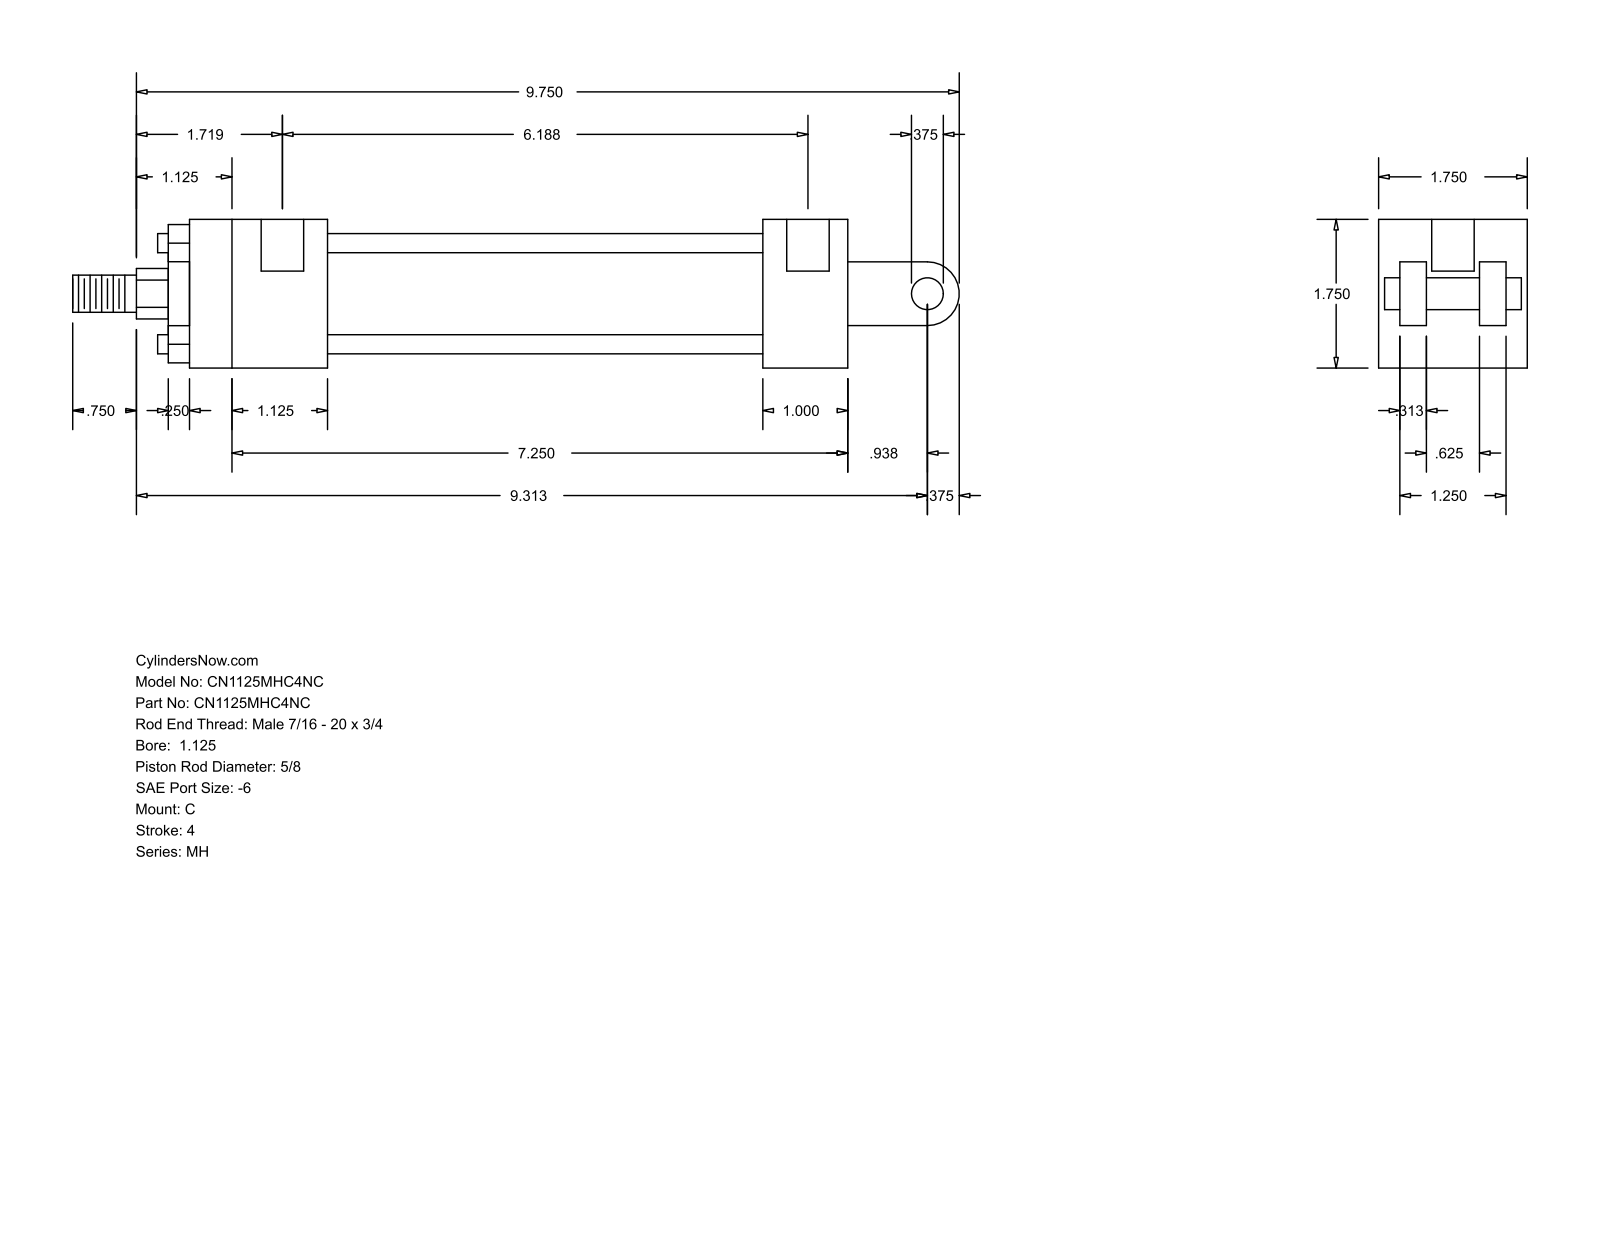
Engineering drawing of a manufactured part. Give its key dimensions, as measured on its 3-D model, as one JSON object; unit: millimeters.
{"part_name": "MH_C__0112_0.625", "step_written_by": "GSSL Pune (CONFIG_CONTROL_DESIGN)", "units": "millimeters", "bodies": {"solids": 0, "faces": 99, "planar": 70, "cylindrical": 29, "other": 0}, "overall_size": [265.11, 44.45, 44.45], "round_holes": [[5.56, 4], [12.7, 2]], "round_bosses_or_shafts": [[5.71, 4], [34.92, 1], [28.57, 1], [15.88, 1], [11.11, 1], [9.53, 1]], "partial_cylinders_radius": [[7.54, 1], [9.53, 1]], "face_to_face_distances": [44.46, 6.35, 31.76, 14.29, 25.4, 30.17, 38.11, 7.94, 23.82, 41.27], "hole_center_spacings": [153.99, 3.17, 157.16]}
